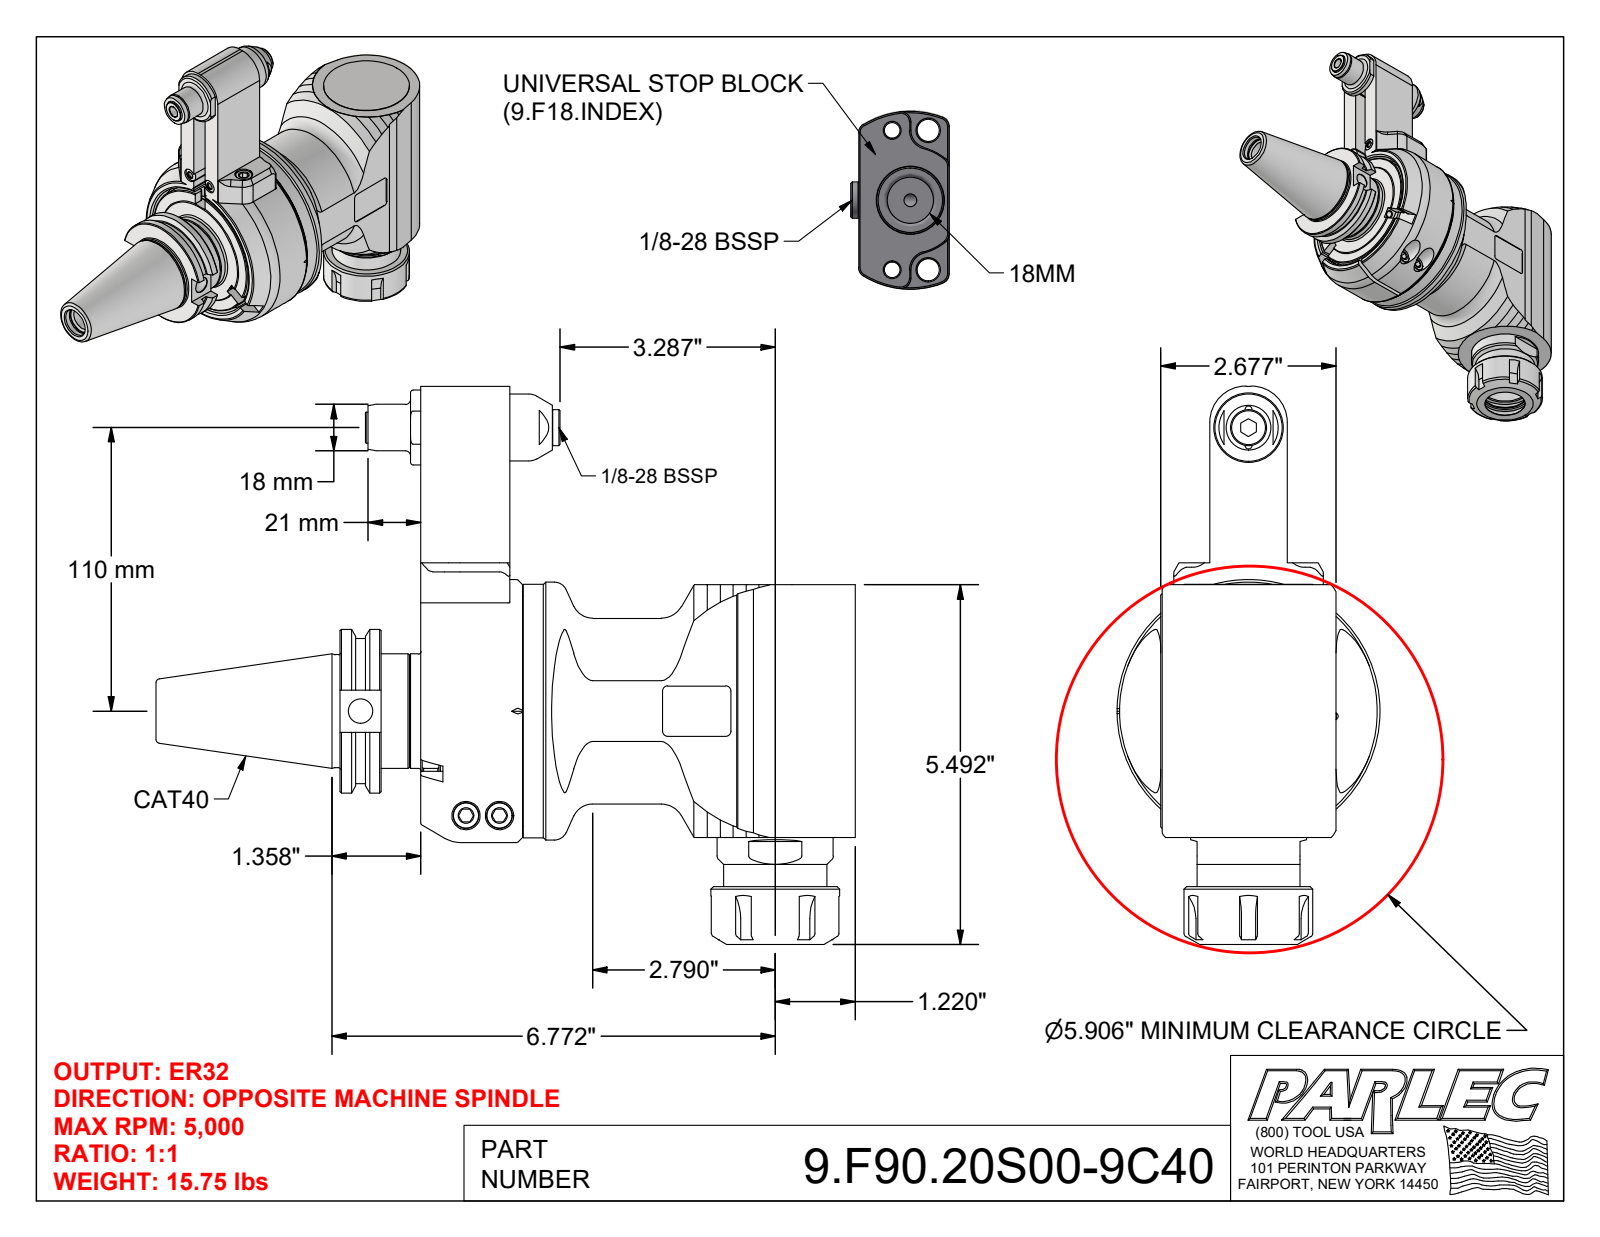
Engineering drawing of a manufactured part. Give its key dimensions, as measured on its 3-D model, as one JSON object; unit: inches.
{"part_name": "9.F90.20S00-9C40; 9_F90_20S00; 9GA11C_441 (Type 1, Cat40, 110mm)", "step_written_by": "Autodesk Inventor 2022 (AUTOMOTIVE_DESIGN)", "units": "inches", "bodies": {"solids": 7, "faces": 666, "planar": 293, "cylindrical": 163, "other": 210}, "overall_size": [10.679, 8.524, 4.016], "volume_in3": 75.01, "surface_area_in2": 269.6, "round_holes": [[0.126, 4], [0.165, 4], [0.256, 3], [0.492, 3], [0.102, 2], [0.13, 2], [0.197, 2], [0.315, 2], [0.409, 2], [0.433, 2], [1.063, 2], [0.098, 1]], "round_bosses_or_shafts": [[0.394, 4], [0.472, 3], [1.575, 2], [0.709, 2], [0.236, 2], [0.098, 2], [4.016, 1], [3.937, 1]], "partial_cylinders_radius": [[0.039, 14], [0.079, 12], [0.118, 6], [0.591, 6], [0.157, 4], [0.02, 2], [0.315, 2], [0.551, 2]], "face_to_face_distances": [1.26, 0.02, 0.748, 1.929, 0.335, 0.276, 1.555, 0.295, 1.28, 0.197], "hole_center_spacings": [0.325, 0.459, 0.276, 0.65, 1.646, 1.674, 1.969, 1.994]}
